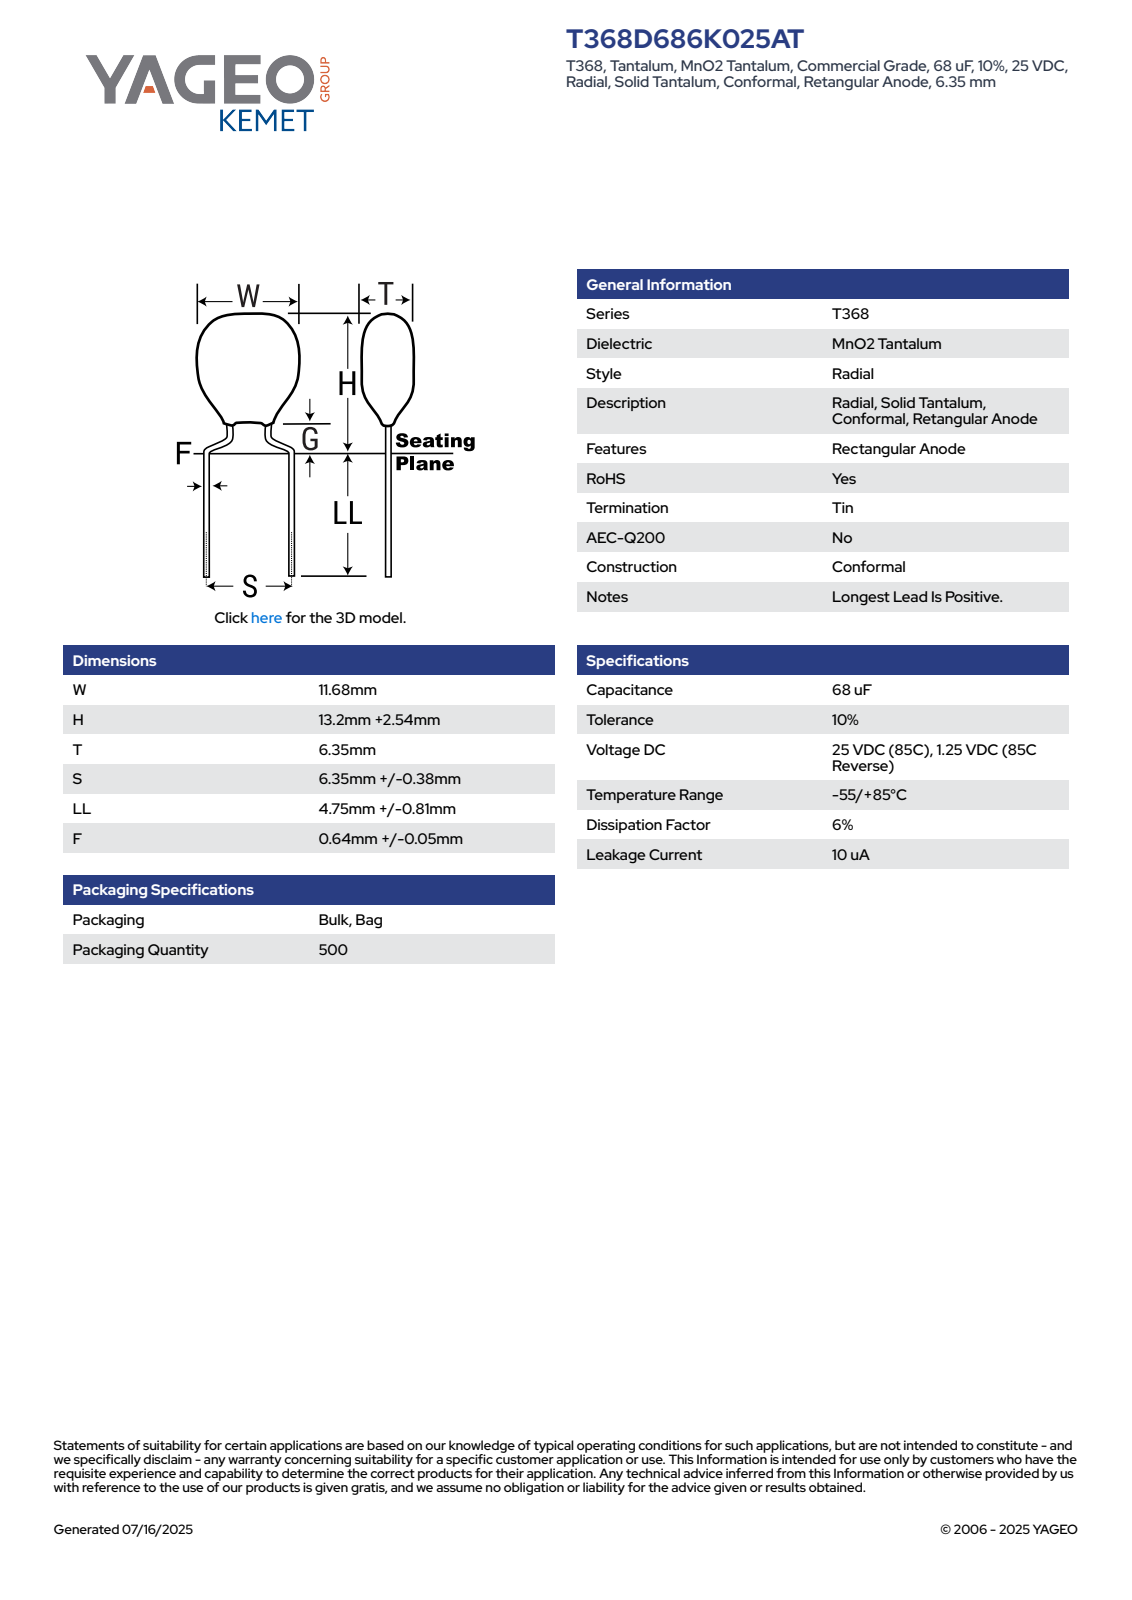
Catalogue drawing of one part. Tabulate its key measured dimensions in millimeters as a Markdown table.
| quantity | value |
| --- | --- |
| part name | CTR_T368_W11.68H15.74T6.35S6.35LL5.56F0.69 |
| STEP written by | SolidWorks 2014 (AUTOMOTIVE_DESIGN) |
| units | millimeters |
| bodies | 4 solids, 142 faces (68 planar, 34 cylindrical, 40 other) |
| overall size | 21.3 × 11.68 × 6.36 |
| volume | 754 mm³ |
| surface area | 508 mm² |
| round bosses / shafts (diameter × count) | 0.69 × 6 |
| partial cylindrical surfaces (radius × count) | 1.4 × 12, 0.3 × 4, 3 × 2, 5 × 2 |
| main face-to-face distances | 6.35, 11.68, 12.12, 9.18, 21.3, 16.09, 6.91, 5.21, 14.68, 5.5 |
